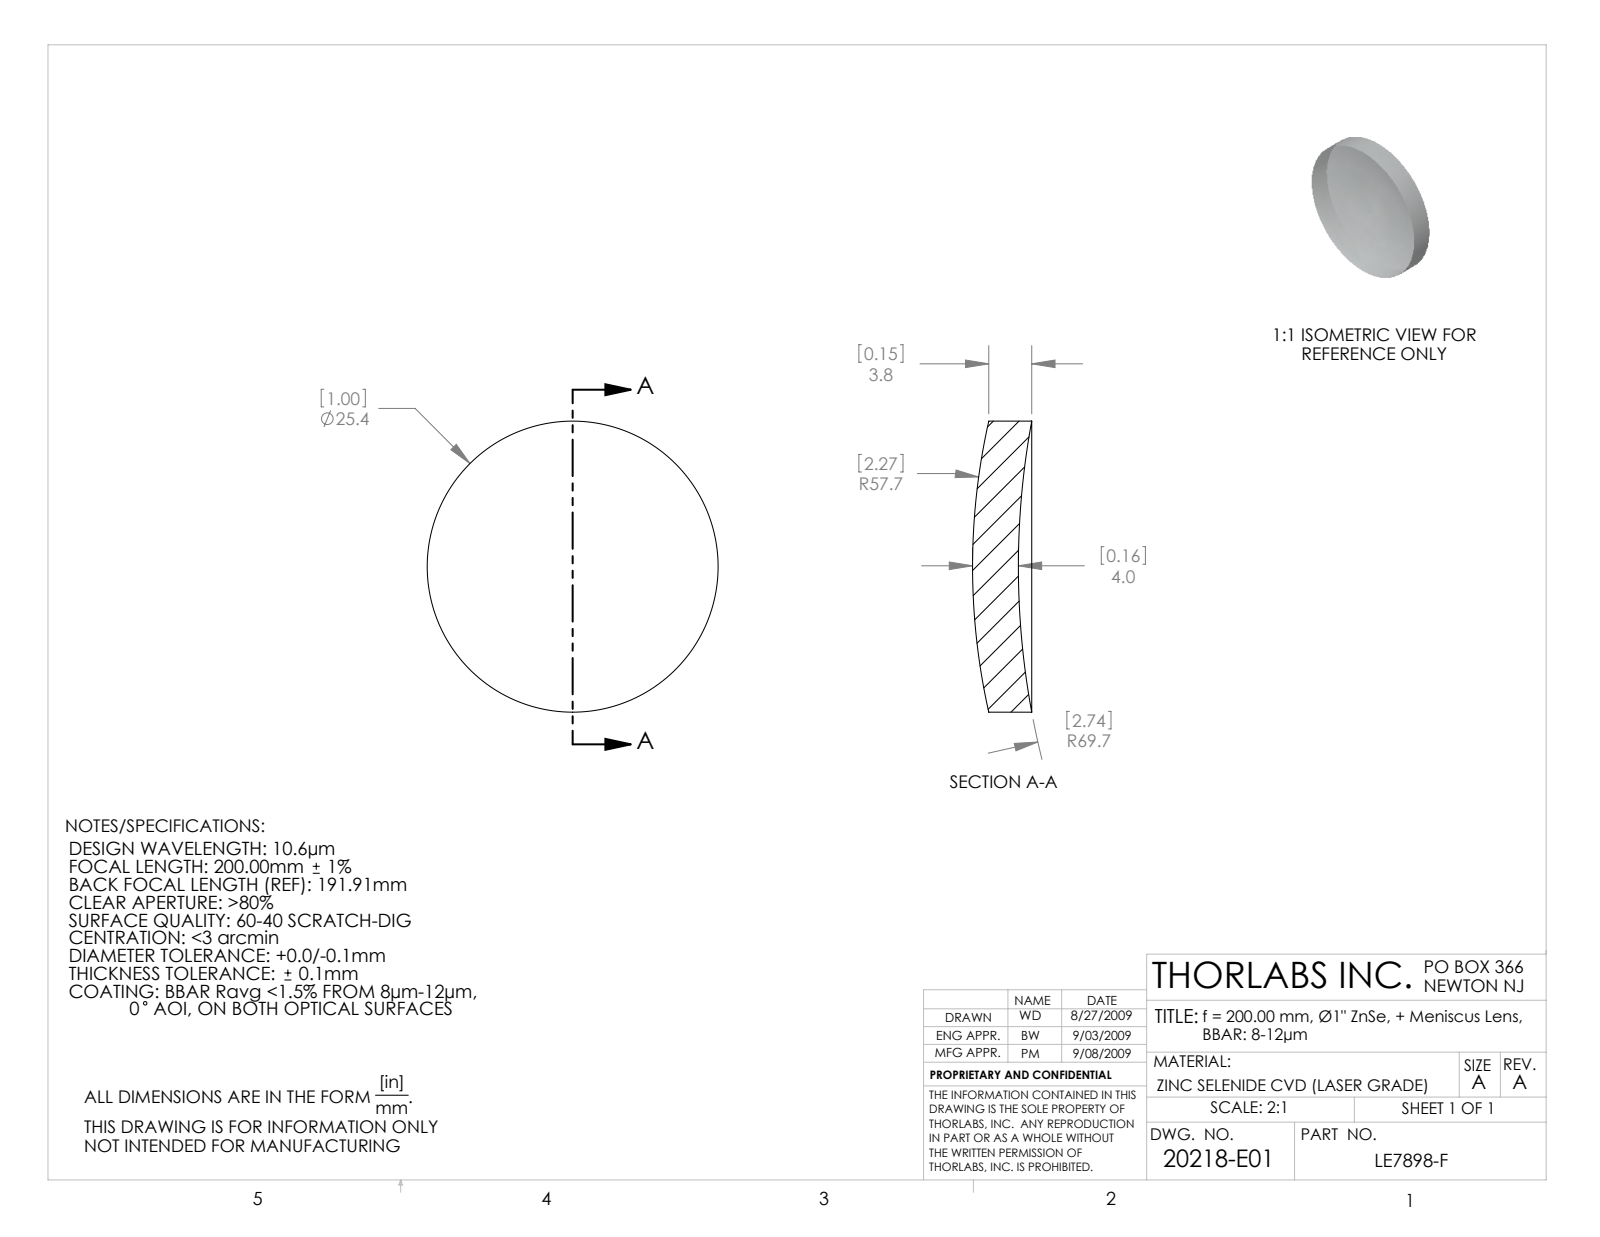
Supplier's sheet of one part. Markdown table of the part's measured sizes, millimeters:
| quantity | value |
| --- | --- |
| part name | 20218-E0W |
| STEP written by | SolidWorks 2007 (CONFIG_CONTROL_DESIGN) |
| units | millimeters |
| bodies | 1 solid, 6 faces (0 planar, 2 cylindrical, 4 other) |
| overall size | 25.4 × 25.4 × 5.17 |
| volume | 1 965 mm³ |
| surface area | 1 323 mm² |
| round bosses / shafts (diameter × count) | 25.4 × 1 |
